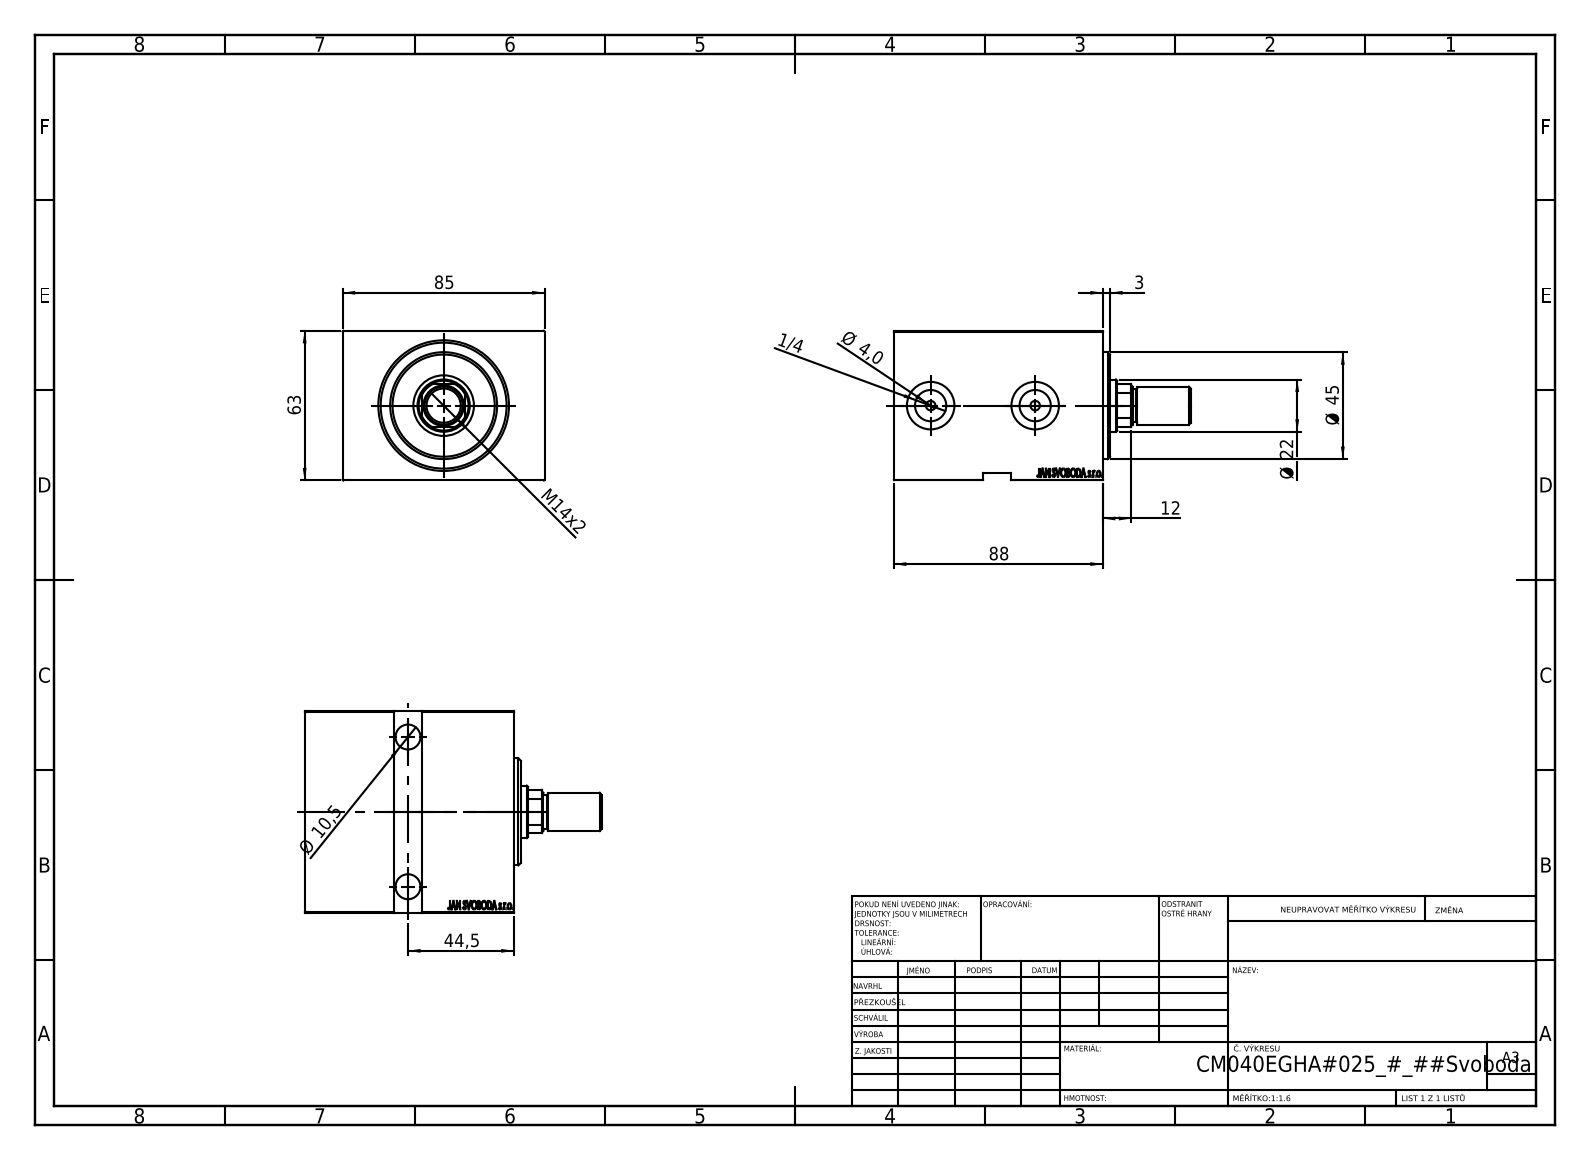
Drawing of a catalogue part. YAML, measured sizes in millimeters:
part_name: "V450CM_E_Body; V450CM_E_VCP; V450CM_VC_B; V450CM_MALE_METRIC"
step_written_by: "SolidWorks 2019 (CONFIG_CONTROL_DESIGN)"
units: millimeters
bodies: {solids: 4, faces: 860, planar: 412, cylindrical: 48, other: 400}
overall_size: [125, 85, 63]
volume: 442976
surface_area: 73452
round_holes:
  - {diameter: 4, count: 2}
  - {diameter: 10.5, count: 2}
  - {diameter: 13.16, count: 2}
  - {diameter: 16.5, count: 2}
  - {diameter: 20, count: 2}
  - {diameter: 12.5, count: 1}
  - {diameter: 22, count: 1}
  - {diameter: 25.5, count: 1}
  - {diameter: 40, count: 1}
  - {diameter: 53, count: 1}
round_bosses_or_shafts:
  - {diameter: 45, count: 1}
  - {diameter: 42, count: 1}
  - {diameter: 16, count: 1}
  - {diameter: 14, count: 1}
partial_cylinders:
  - {radius: 10.5, count: 1}
face_to_face_distances: [63, 85, 88, 12, 76, 3, 5, 83, 71, 37]
hole_center_spacings: [44, 63]
